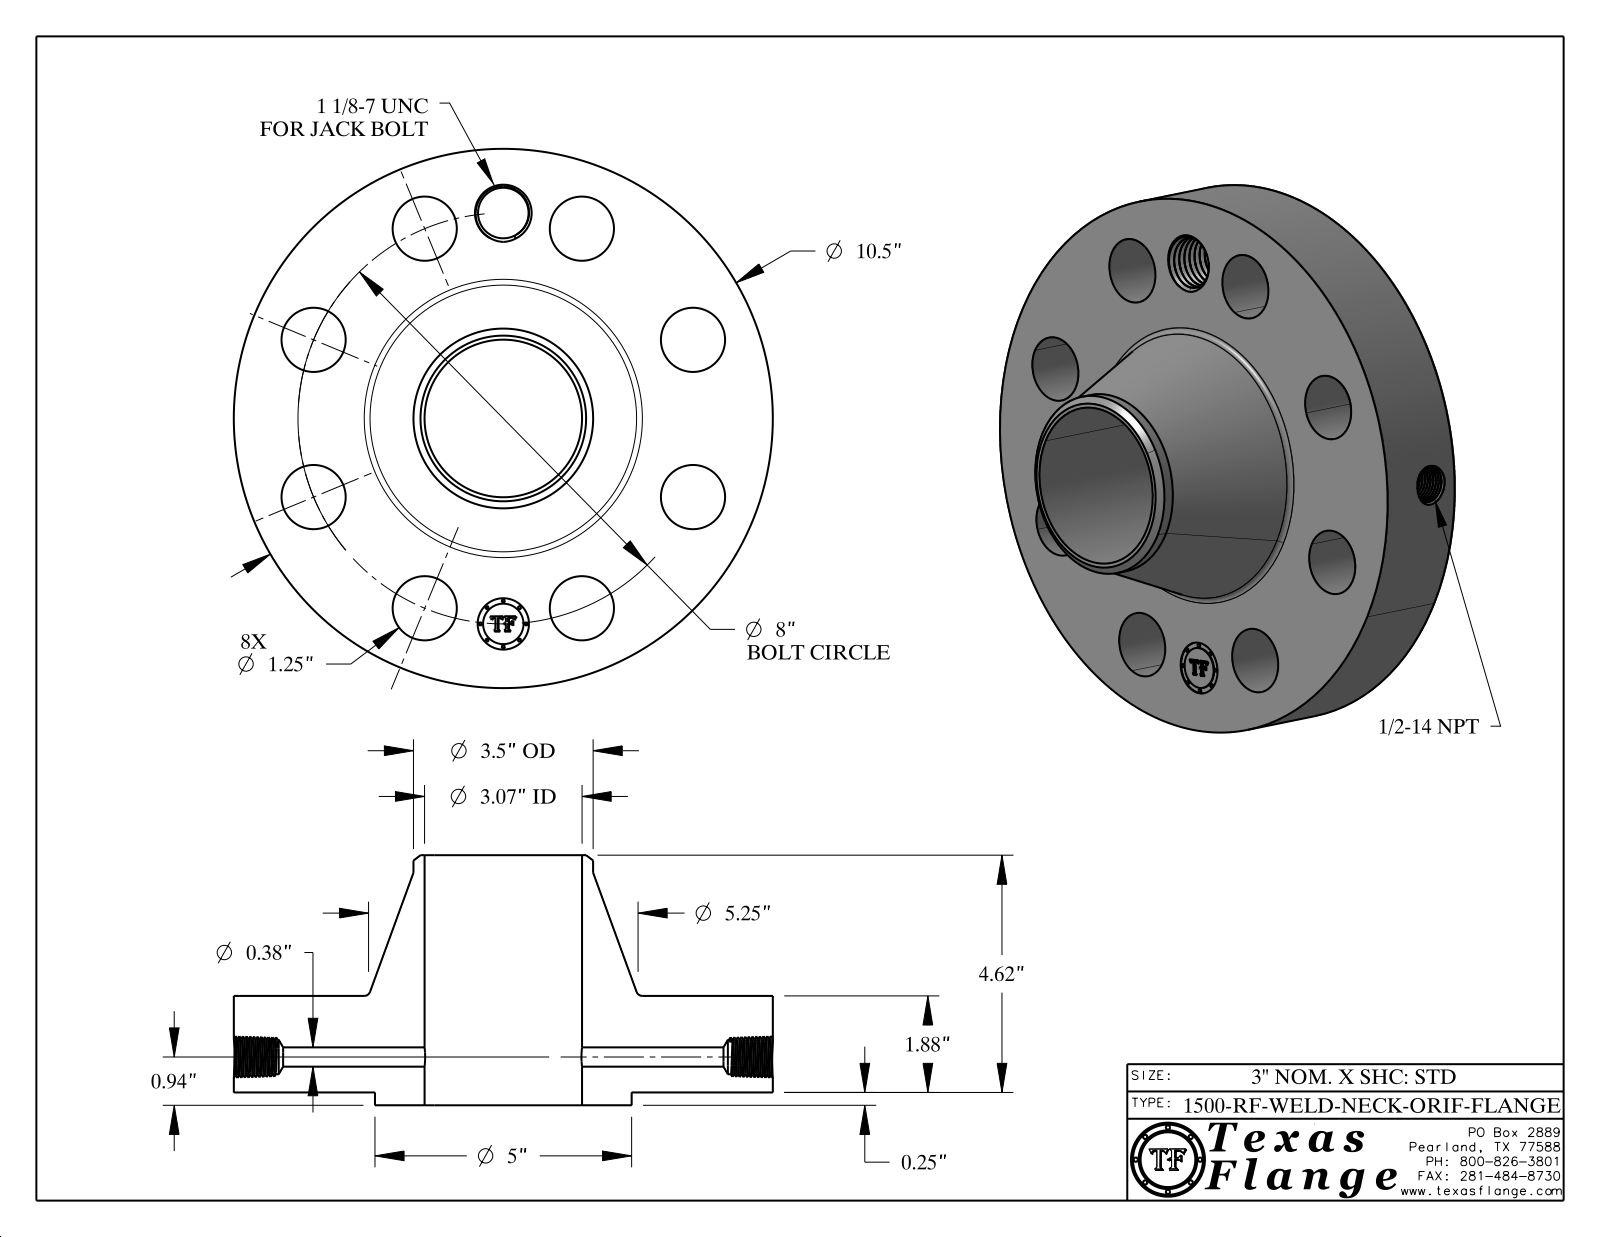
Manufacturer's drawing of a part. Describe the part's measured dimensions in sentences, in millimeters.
The part is named "1500-RF-WELD-NECK". Its 3-D file was written by "CATIA V5 STEP AP214 (AUTOMOTIVE_DESIGN)". It is 1 solid with 760 faces: 369 planar, 90 cylindrical and 301 other. Overall it measures 266.7 by 266.7 by 123.7 millimeters. Its volume is 2 458 000 cubic millimeters and its surface area 230 100 square millimeters. Round holes: 8 of diameter 31.8, 1 of diameter 9.5, 1 of diameter 17.1, 1 of diameter 25, 1 of diameter 25.4, 1 of diameter 77.9. Round bosses or shafts: 8 of diameter 1.5, 1 of diameter 266.7, 1 of diameter 127, 1 of diameter 88.9, 1 of diameter 20. The main face-to-face distances are 47.8, 6.4, 54.1, 123.7, 117.3, 69.6, 53.7, 47.4, 0.4, 70. The hole center spacings are 101.6, 143.7, 187.7, 39.6, 77.7, 77.8, 112.9, 169.
